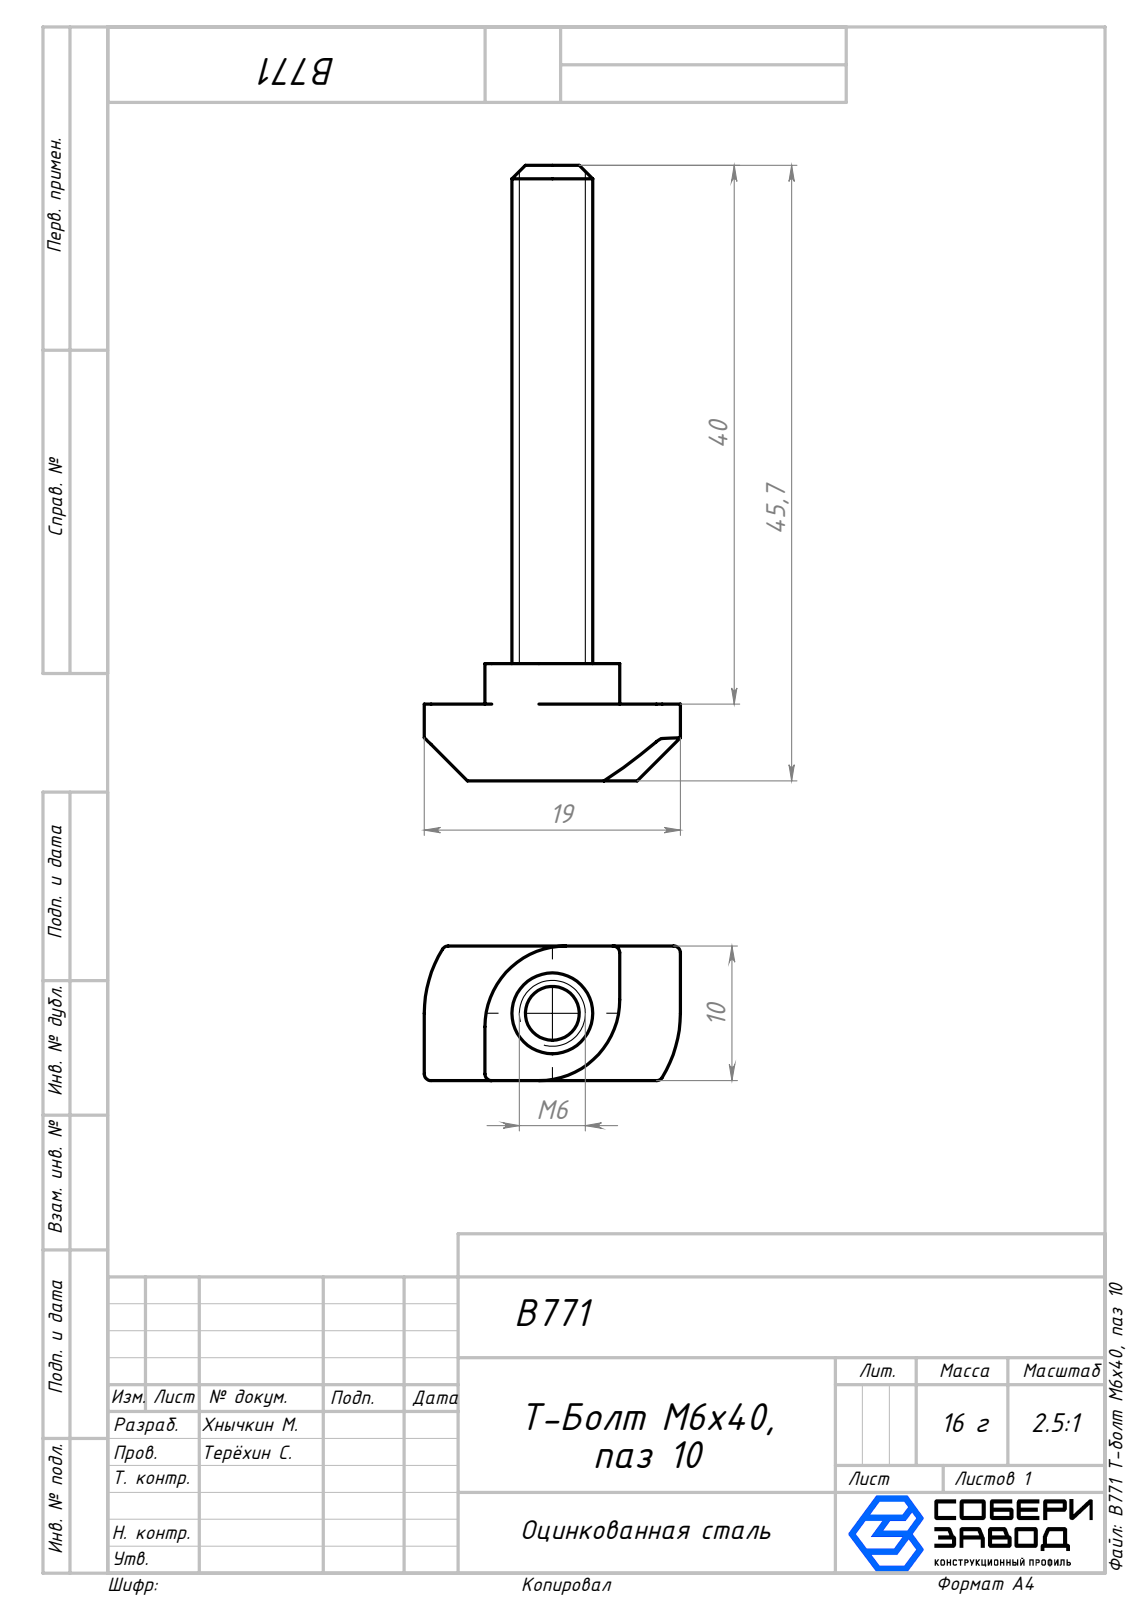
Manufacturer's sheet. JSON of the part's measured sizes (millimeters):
{"part_name": "B771 Т-болт М6х40, паз 10", "step_written_by": "SolidWorks 2025 (AUTOMOTIVE_DESIGN)", "units": "millimeters", "bodies": {"solids": 1, "faces": 29, "planar": 13, "cylindrical": 12, "other": 4}, "overall_size": [45.7, 19, 10], "volume_mm3": 2241, "surface_area_mm2": 1413, "round_bosses_or_shafts": [[6, 1]], "partial_cylinders_radius": [[0.5, 6], [6, 2], [9.08, 2]], "face_to_face_distances": [10, 5.7, 8.7, 3, 4.5, 14.5, 45.7, 40, 37, 19]}
